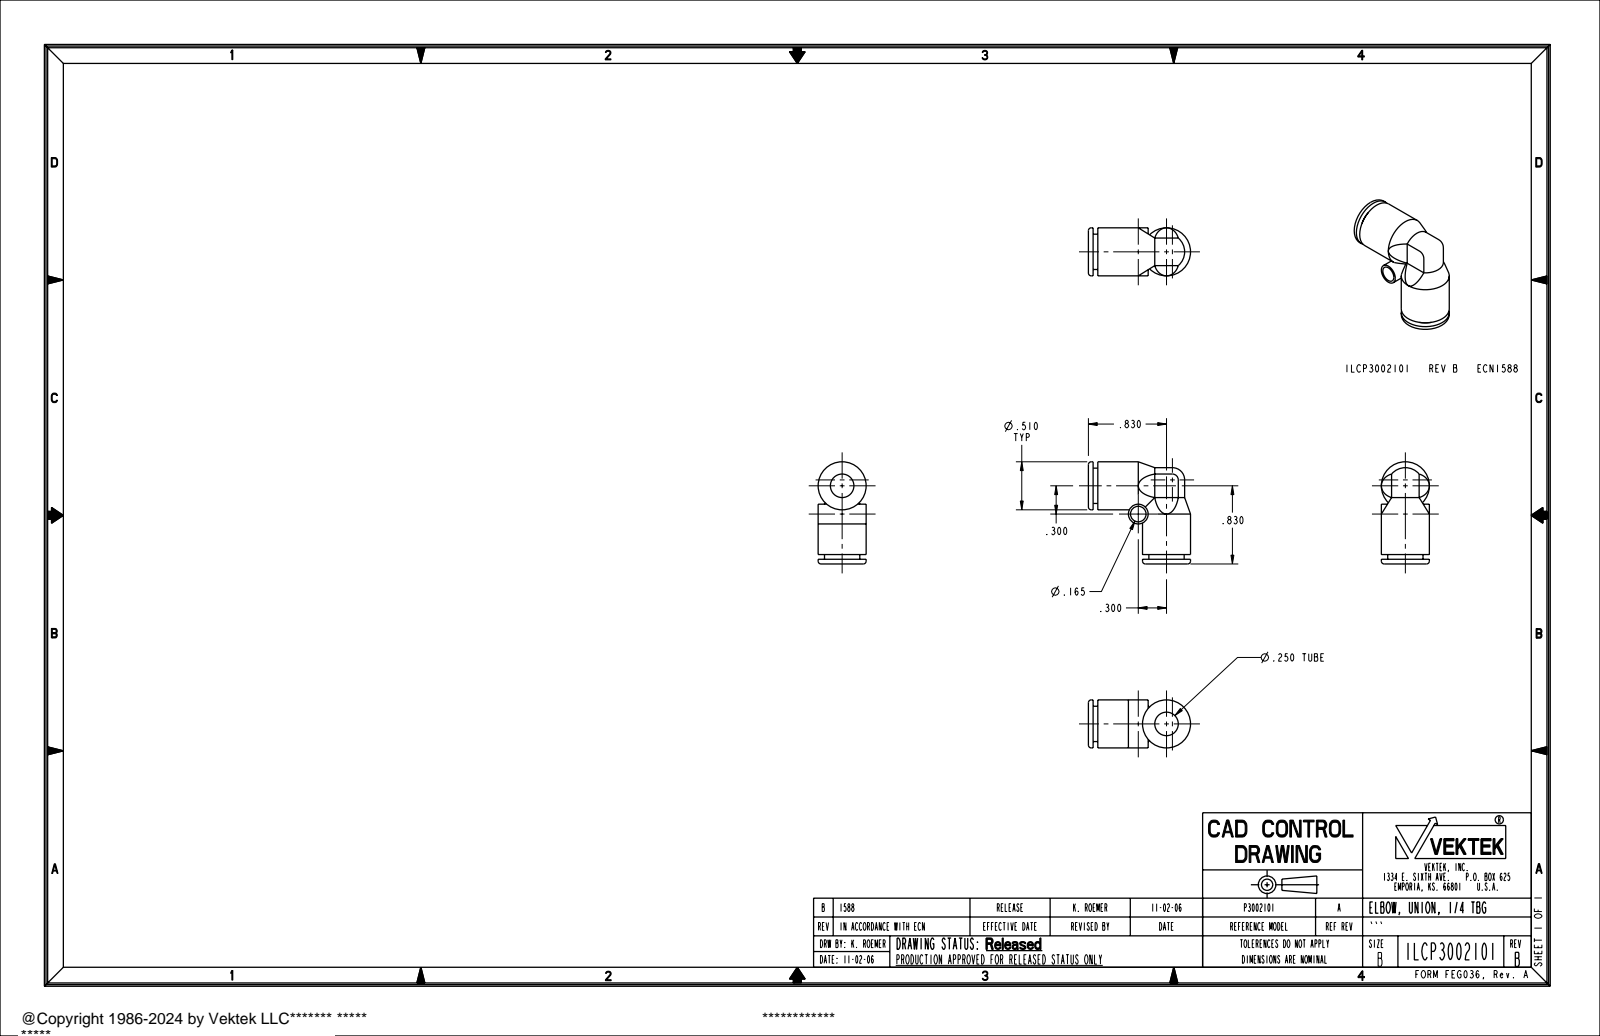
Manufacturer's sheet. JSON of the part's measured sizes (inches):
{"part_name": "ILCP3002101", "step_written_by": "PRO/ENGINEER BY PARAMETRIC TECHNOLOGY CORPORATION, 2005180 (AUTOMOTIVE_DESIGN_CC2)", "units": "inches", "bodies": {"solids": 1, "faces": 53, "planar": 16, "cylindrical": 26, "other": 11}, "overall_size": [1.085, 1.085, 0.51], "volume_in3": 0.204, "surface_area_in2": 4.862, "round_holes": [[0.25, 2], [0.165, 1]], "round_bosses_or_shafts": [[0.51, 2], [0.375, 2], [0.21, 1]], "partial_cylinders_radius": [[0.192, 2]], "face_to_face_distances": [0.05, 0.1, 0.955, 0.905, 0.855, 0.293, 0.109, 0.402, 0.51]}
